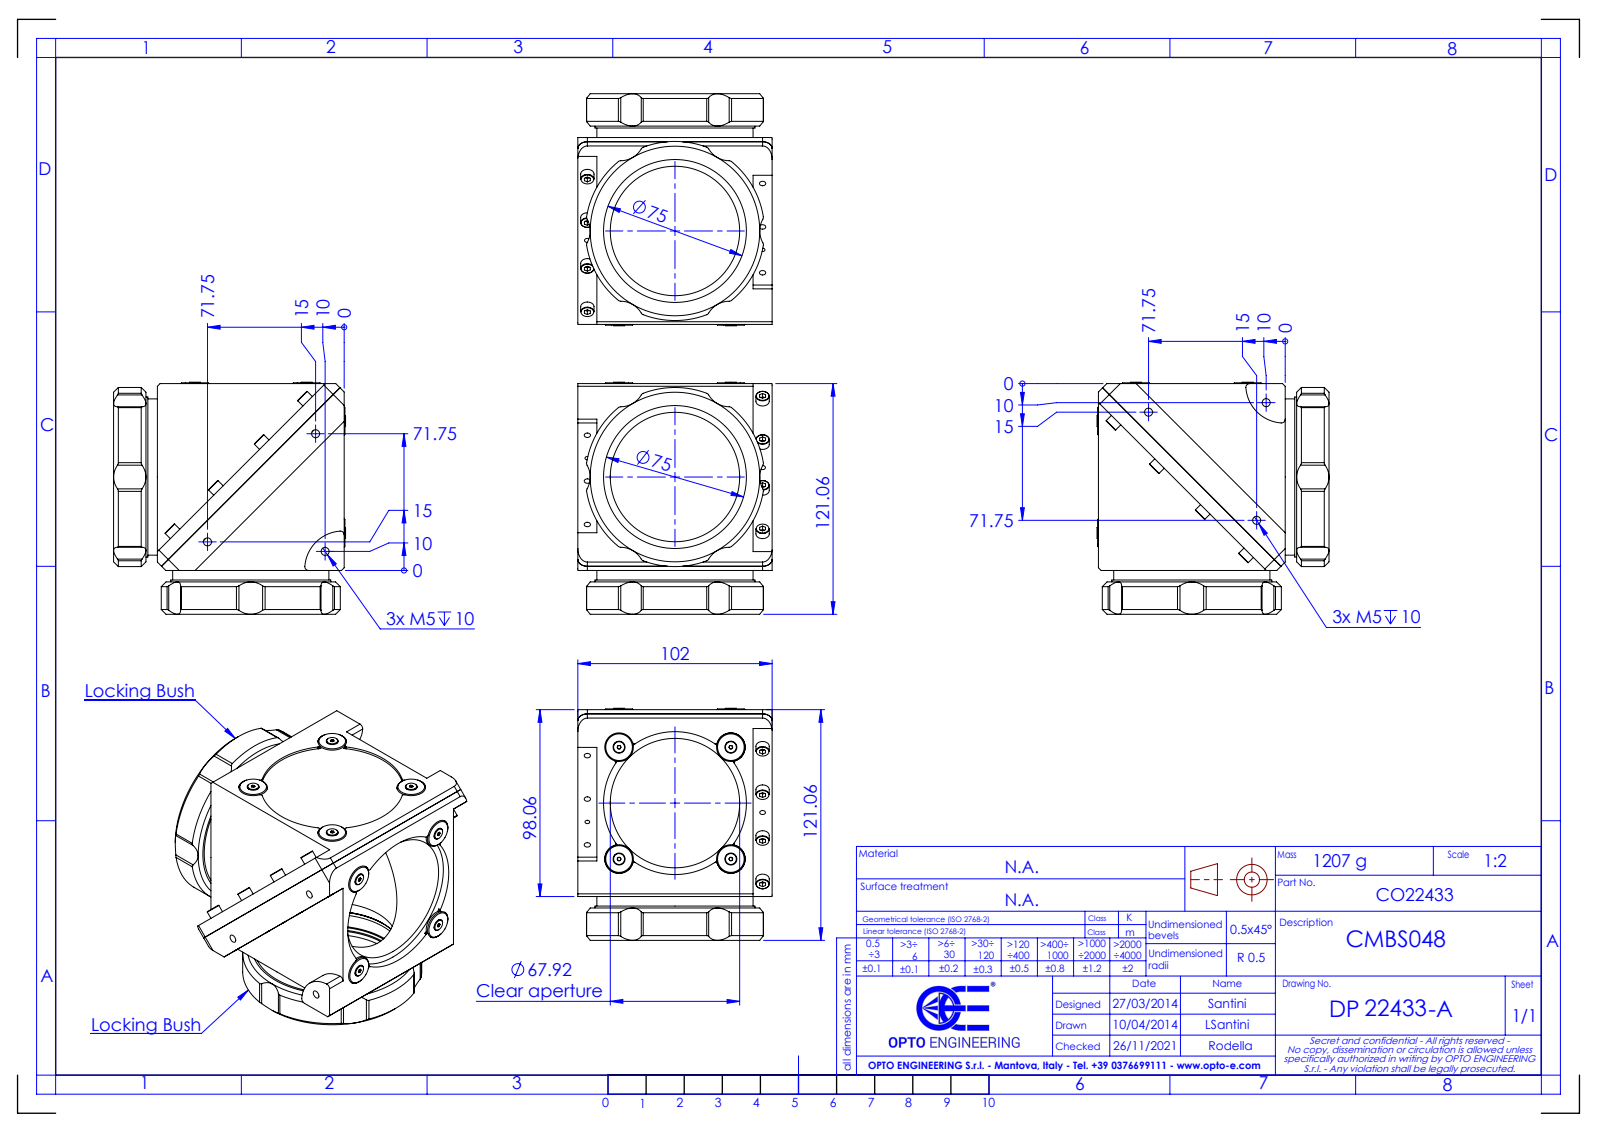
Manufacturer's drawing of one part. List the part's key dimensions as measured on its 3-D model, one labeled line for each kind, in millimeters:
Part name (STEP PRODUCT): DP22433 -A_CMBS048
STEP written by: SolidWorks 2021 (CONFIG_CONTROL_DESIGN)
Units: millimetres
Bodies: 0 solids, 532 faces (174 planar, 242 cylindrical, 116 other)
Overall size (bounding box): 121.79 × 121.79 × 102
Round holes (diameter × count): ⌀3.3 ×8, ⌀4.2 ×6, ⌀15 ×4, ⌀2.5 ×2, ⌀3 ×2, ⌀67.92 ×2, ⌀75 ×2, ⌀75.6 ×2, ⌀77.2 ×2, ⌀79 ×2, ⌀82 ×2, ⌀84 ×1
Round bosses / shafts (diameter × count): ⌀7 ×8, ⌀5.75 ×8, ⌀15 ×4, ⌀84 ×1
Partial cylindrical surfaces — rounded edges, fillets, slot ends (radius × count): R2 ×28, R1 ×16, R12.5 ×12, R5 ×4, R25 ×4, R20 ×2, R47 ×2
Main face-to-face distances: 2, 10, 82, 98.06, 92, 3, 7, 94.06, 4, 1
Hole centre spacings: 92, 17, 32.23, 41.49, 49.23, 61.95, 66.23, 74.86
